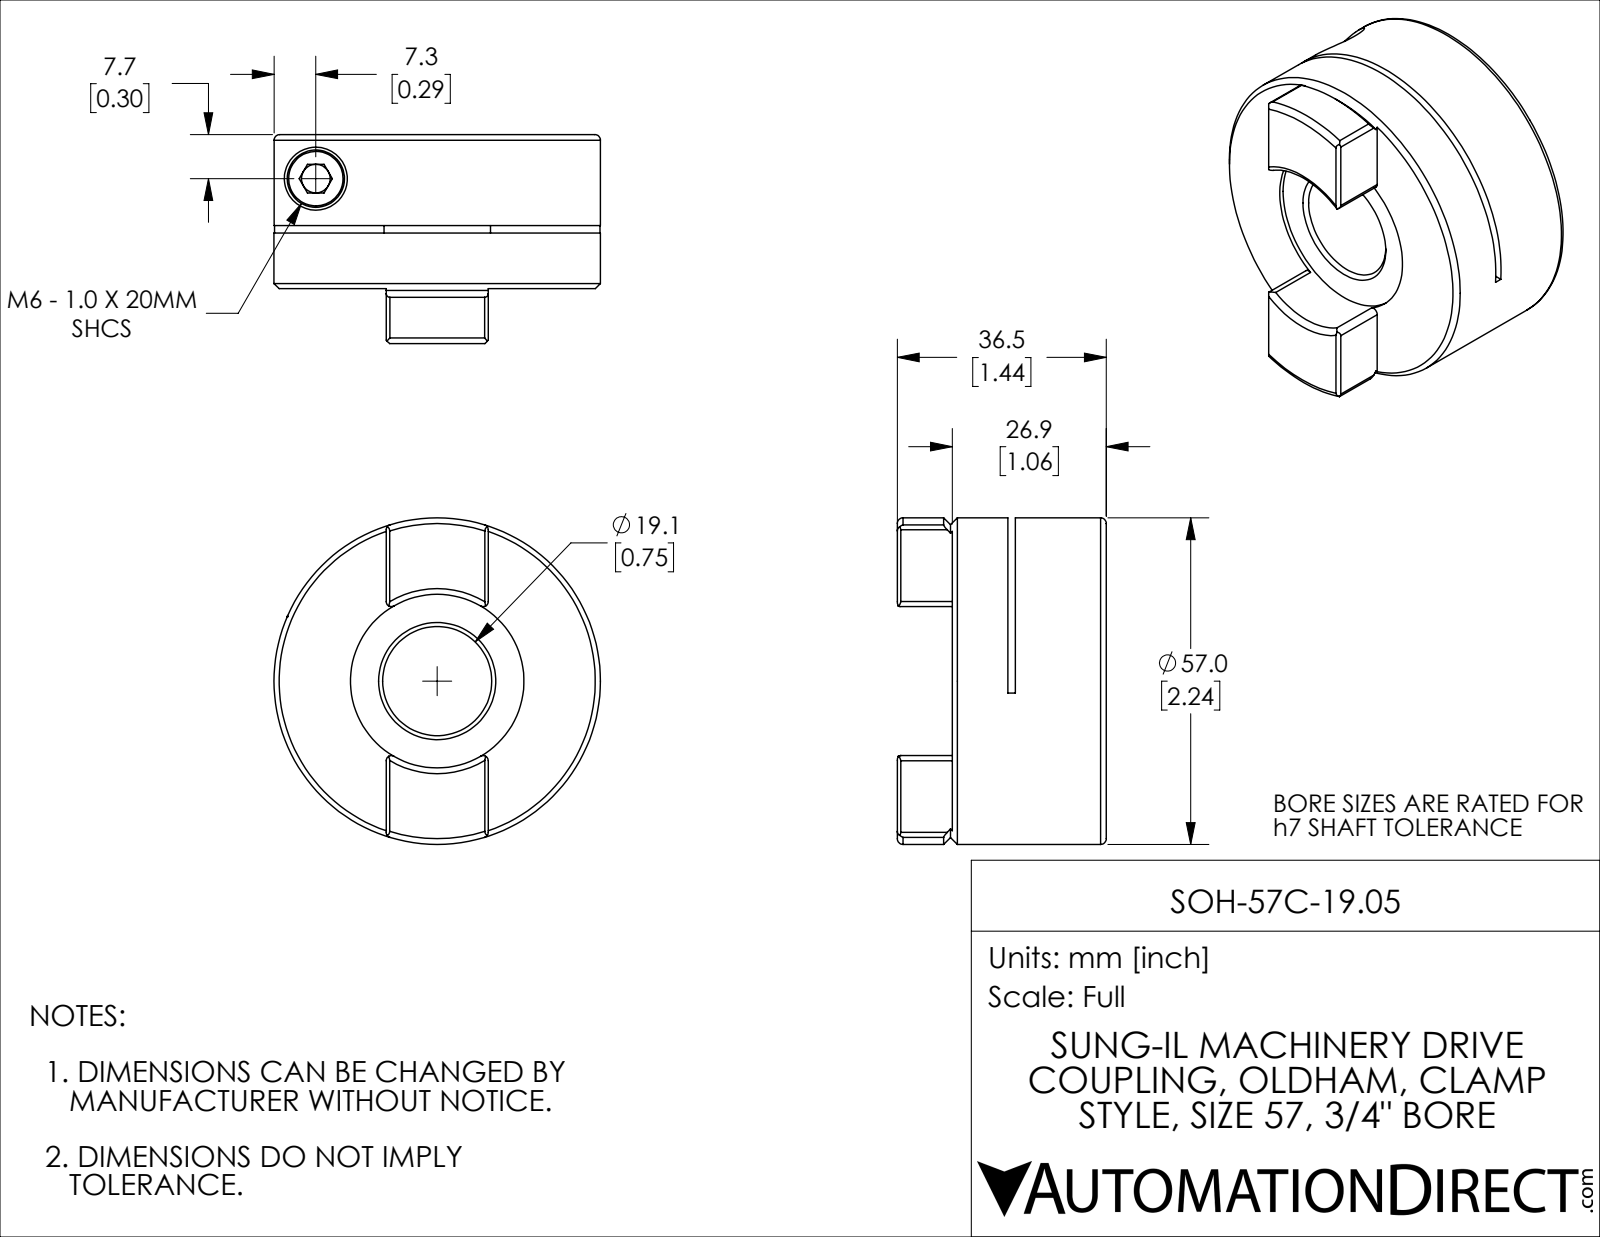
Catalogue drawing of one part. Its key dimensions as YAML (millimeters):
part_name: "SOH-57C-19.05"
step_written_by: "SolidWorks 2021 (CONFIG_CONTROL_DESIGN)"
units: millimeters
bodies: {solids: 2, faces: 99, planar: 39, cylindrical: 33, other: 27}
overall_size: [57, 57, 36.5]
volume: 62210
surface_area: 16430
round_holes:
  - {diameter: 5, count: 1}
  - {diameter: 6.4, count: 1}
  - {diameter: 11, count: 1}
  - {diameter: 19.1, count: 1}
  - {diameter: 30.3, count: 1}
round_bosses_or_shafts:
  - {diameter: 57, count: 1}
  - {diameter: 10, count: 1}
  - {diameter: 6, count: 1}
partial_cylinders:
  - {radius: 0.9, count: 8}
  - {radius: 40, count: 1}
face_to_face_distances: [1.3, 26.9, 17.2, 9.7, 15.9, 11, 10.2, 26.1, 8.9, 0.8]
